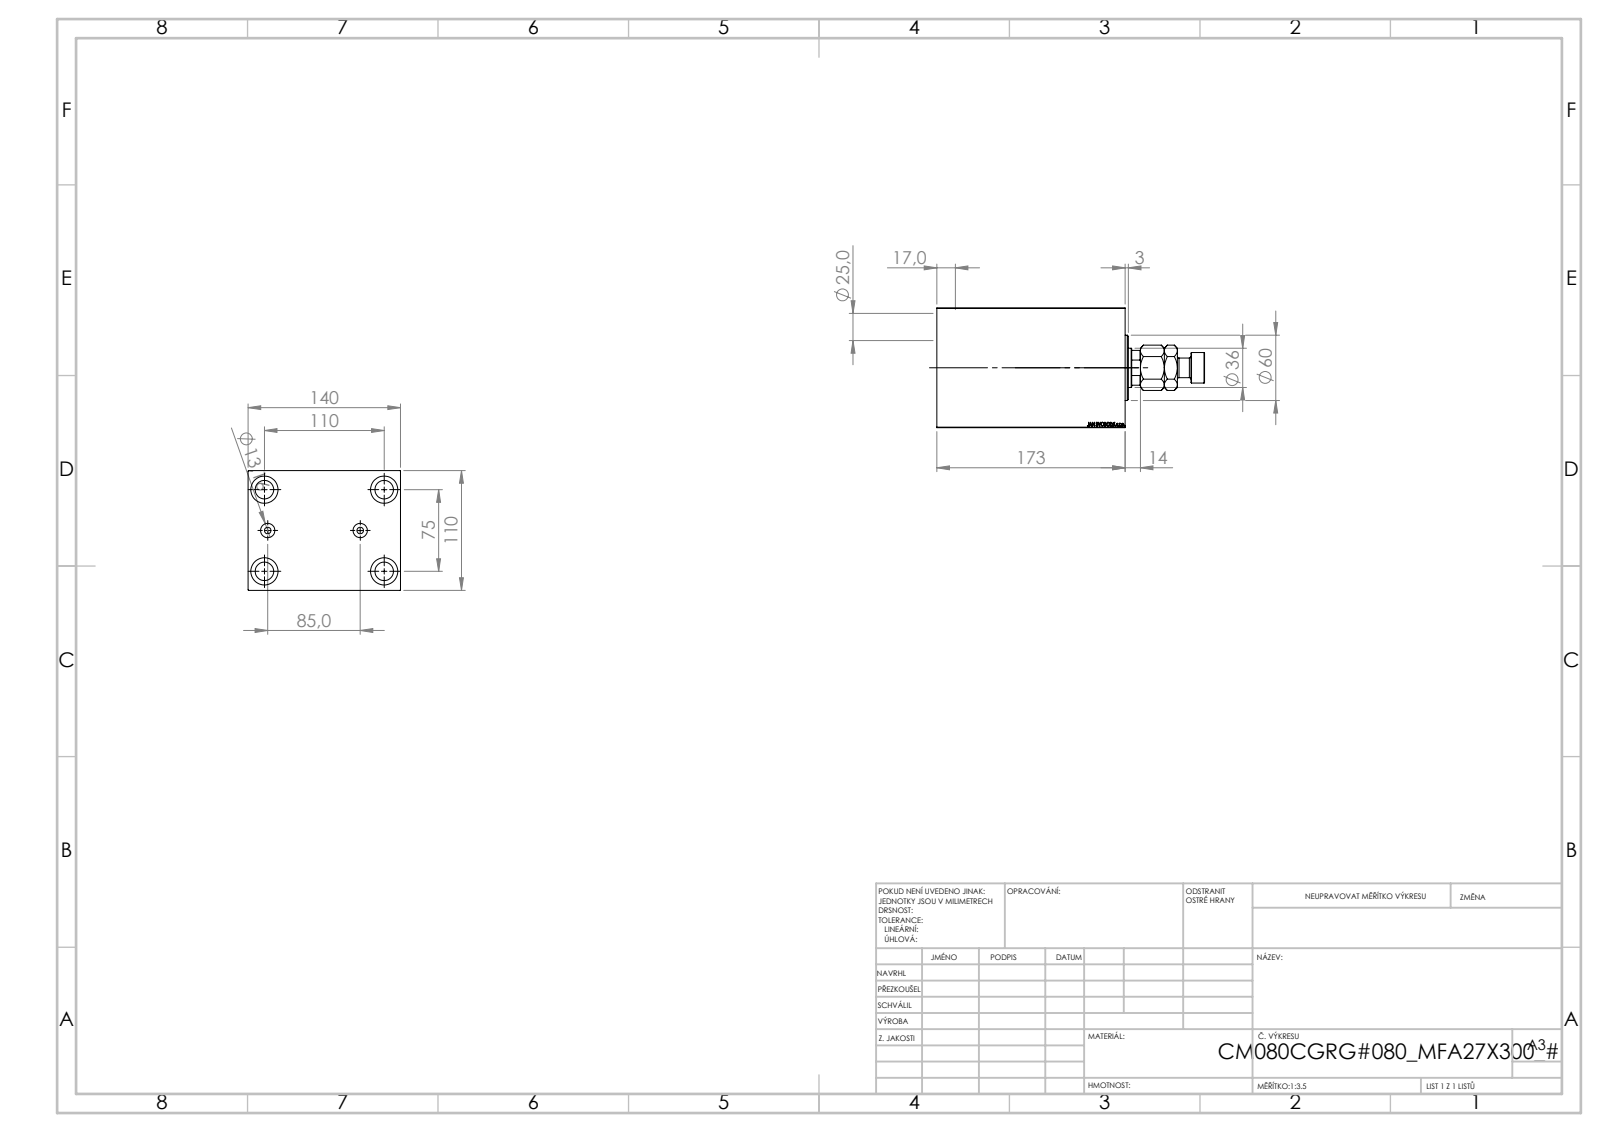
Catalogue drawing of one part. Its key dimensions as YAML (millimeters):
part_name: "V450CM_C_Body; V450CM_VC_B; V450CM_C_VCP; MFA"
step_written_by: "SolidWorks 2019 (CONFIG_CONTROL_DESIGN)"
units: millimeters
bodies: {solids: 4, faces: 915, planar: 427, cylindrical: 62, other: 426}
overall_size: [246, 140, 110]
volume: 2189000
surface_area: 268169
round_holes:
  - {diameter: 17, count: 4}
  - {diameter: 25, count: 4}
  - {diameter: 6, count: 2}
  - {diameter: 13.16, count: 2}
  - {diameter: 25.5, count: 1}
  - {diameter: 36, count: 1}
  - {diameter: 39.5, count: 1}
  - {diameter: 80, count: 1}
  - {diameter: 82, count: 1}
  - {diameter: 87, count: 1}
round_bosses_or_shafts:
  - {diameter: 60, count: 1}
  - {diameter: 28, count: 1}
  - {diameter: 18, count: 1}
partial_cylinders:
  - {radius: 17.5, count: 1}
face_to_face_distances: [110, 140, 173, 152, 21, 37.3, 114.7, 135.7, 117.3, 80]
hole_center_spacings: [39.53, 66.57, 104.46, 42.5, 75, 110, 133.14, 85]
